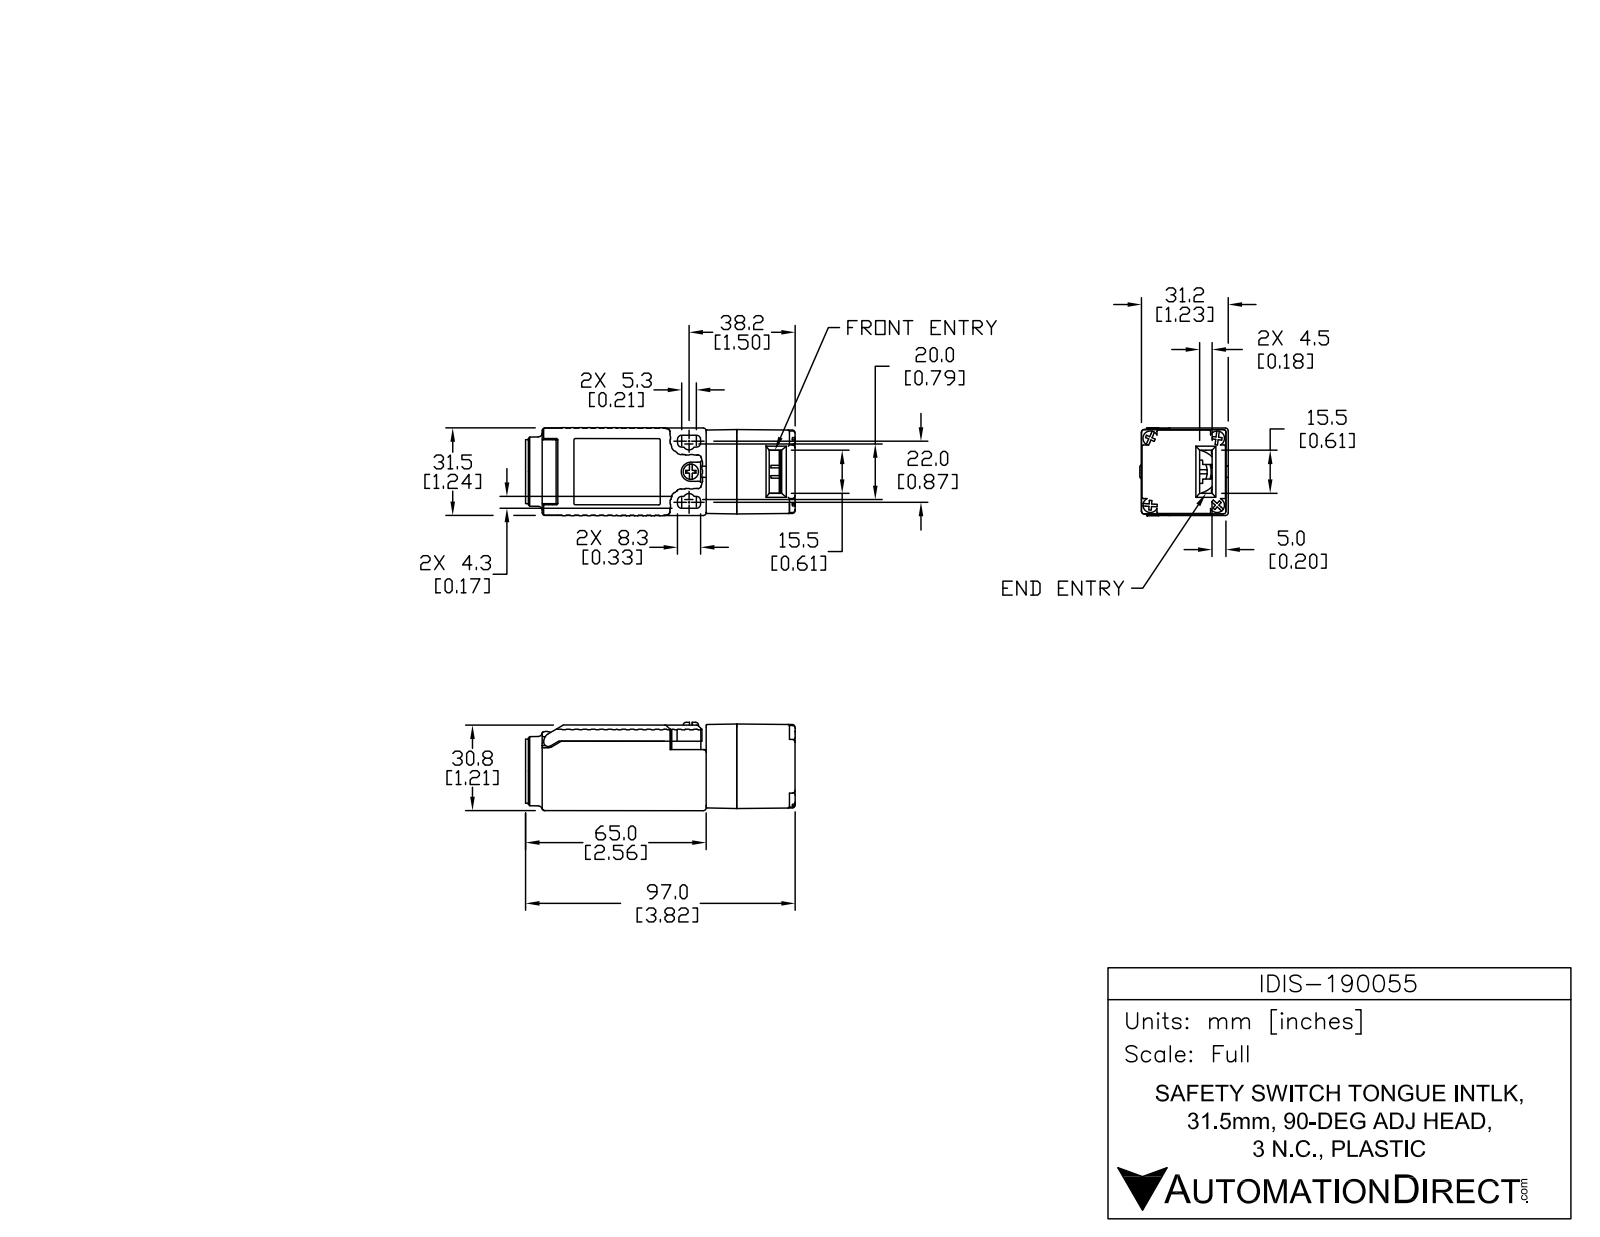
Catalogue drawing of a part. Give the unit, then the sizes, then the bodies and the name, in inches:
Units: inches
Overall size (bounding box): 4.055 × 1.268 × 1.24
Round holes (diameter × count): ⌀0.157 ×2, ⌀0.637 ×1, ⌀0.728 ×1, ⌀0.835 ×1
Round bosses / shafts (diameter × count): ⌀0.197 ×5, ⌀0.984 ×1, ⌀0.906 ×1, ⌀0.677 ×1
Partial cylindrical surfaces — rounded edges, fillets, slot ends (radius × count): R0.02 ×27, R0.039 ×21, R0.01 ×20, R0.059 ×8, R0.094 ×6, R0.118 ×4, R0.017 ×2, R0.079 ×2
Main face-to-face distances: 1.24, 0.02, 1.189, 0.039, 1.196, 1.195, 0.197, 0.098, 1.181, 0.22
Hole centre spacings: 0.866
Volume: 5.153 in³ · Surface area: 30.12 in²
Bodies: 1 solid, 475 faces (228 planar, 170 cylindrical, 77 other)
Part name (STEP PRODUCT): IDIS-190055
STEP written by: SolidWorks 2013 (AUTOMOTIVE_DESIGN)
